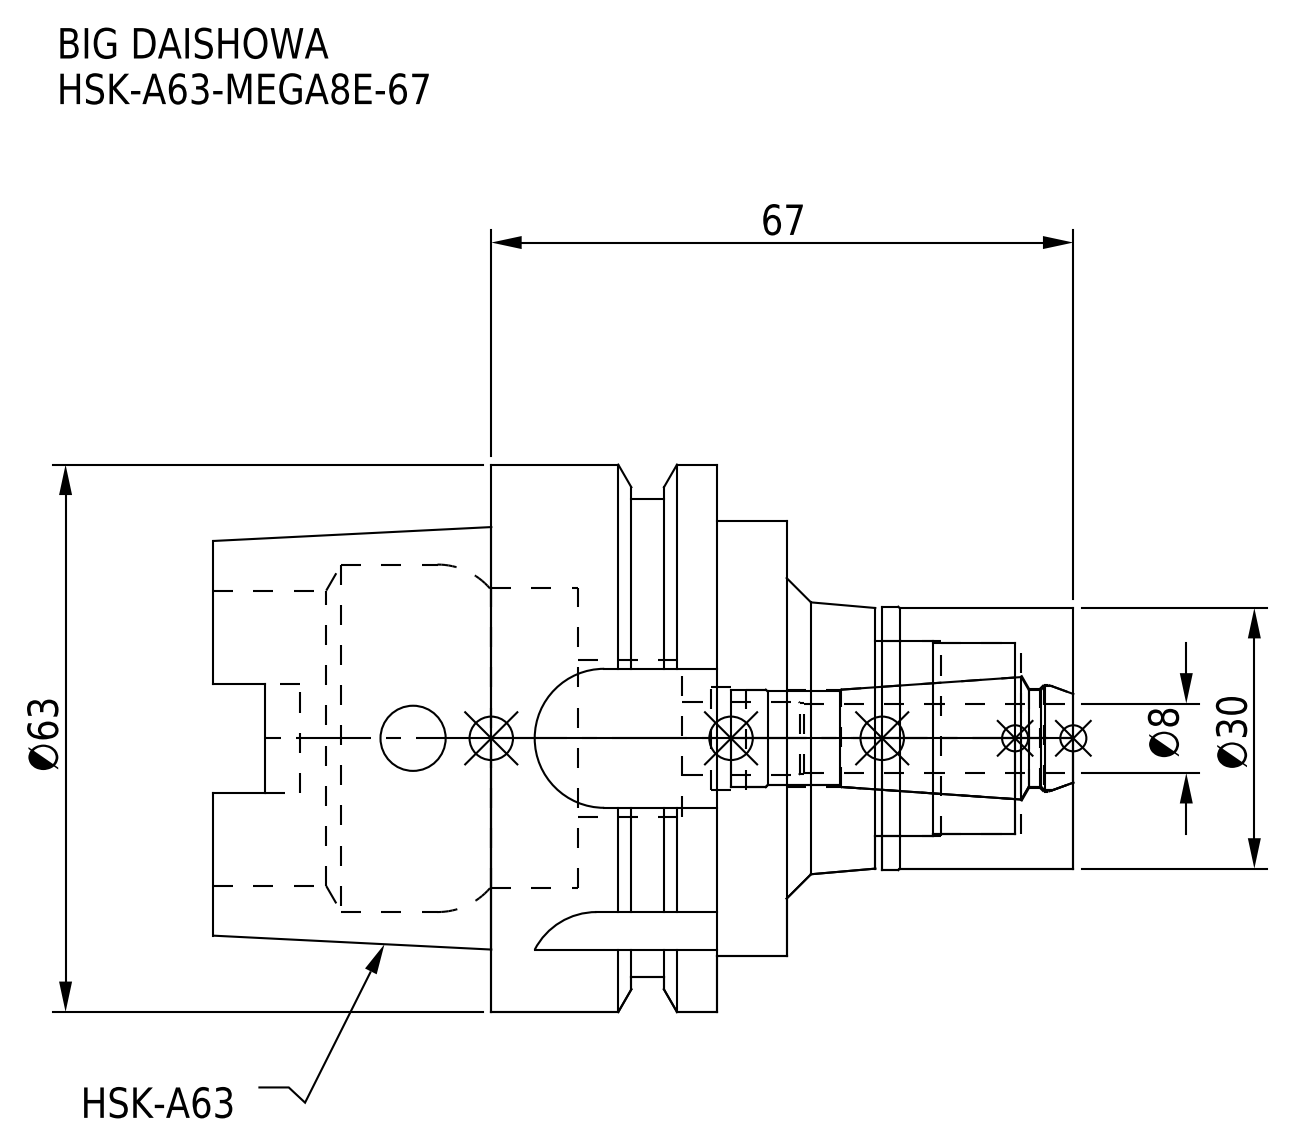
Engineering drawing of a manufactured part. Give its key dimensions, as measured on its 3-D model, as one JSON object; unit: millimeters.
{"part_name": "HSK-A63-MEGA8E-67-080-FreeParts; MEN8_1.stp; DXF_TEMP_ASSY_ASM_4_ASM.stp; HSK-A63-MEGA8E-67 (+3 more)", "step_written_by": "SolidWorks 2019 (CONFIG_CONTROL_DESIGN)", "units": "millimeters", "bodies": {"solids": 2, "faces": 126, "planar": 44, "cylindrical": 54, "other": 28}, "overall_size": [99, 63, 63], "volume_mm3": 116422, "surface_area_mm2": 31403, "round_holes": [[7.5, 1], [8.39, 1], [8.4, 1], [11.2, 1], [11.4, 1], [11.8, 1], [12.3, 1], [18, 1], [22, 1], [22.5, 1], [34, 1], [34.5, 1]], "round_bosses_or_shafts": [[63, 1], [55, 1], [50, 1], [30.3, 1], [30, 1]], "partial_cylinders_radius": [[2.8, 2], [2.88, 2], [8, 2], [9, 1]], "face_to_face_distances": [26, 8, 34, 67, 24.05, 16.05, 9.95, 33, 41, 57.05]}
